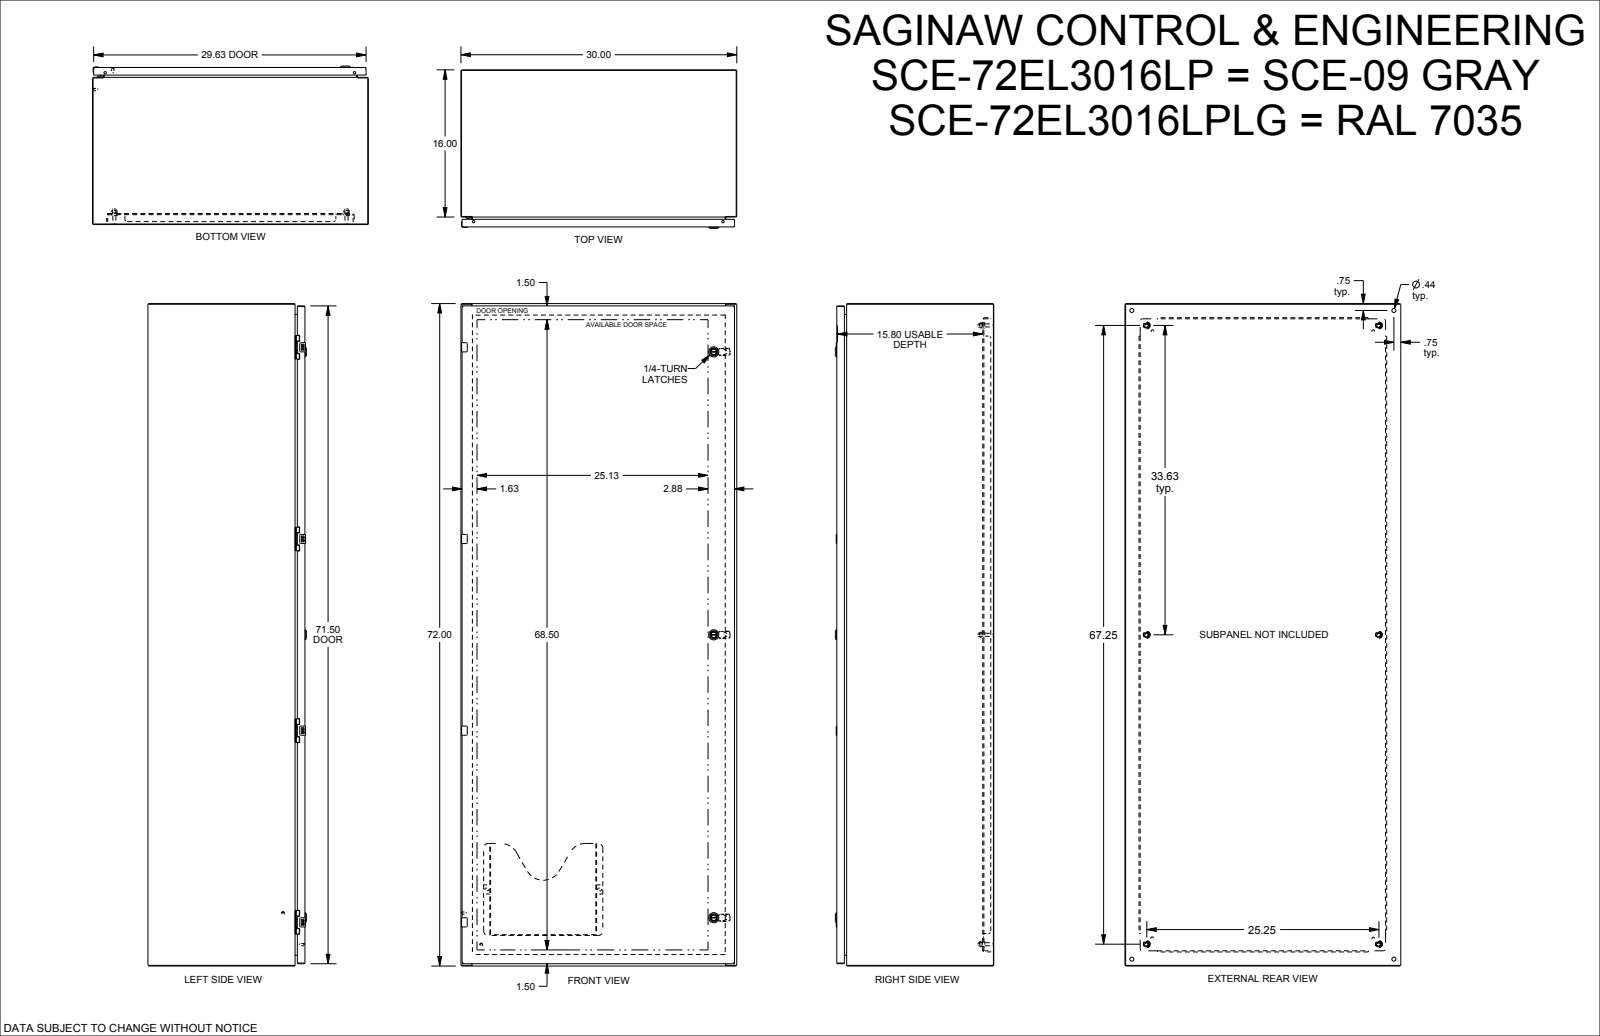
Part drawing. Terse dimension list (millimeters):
name: SCE-72EL3016LP
written by: SolidWorks 2019 (CONFIG_CONTROL_DESIGN)
unit: mm
bodies: 0 solids, 4259 faces (2033 planar, 1208 cylindrical, 1018 other)
size: 1828.8 × 762 × 437.6
holes: 10× ⌀6.8, 8× ⌀4.4, 8× ⌀5.2, 8× ⌀6.2, 8× ⌀9.5, 6× ⌀9.3, 6× ⌀12.7, 4× ⌀1, 4× ⌀4, 4× ⌀5.5, 4× ⌀7.1, 4× ⌀11.1
bosses: 12× ⌀4.3, 8× ⌀6.4, 8× ⌀6.1, 6× ⌀9.3, 6× ⌀8.4, 5× ⌀5, 4× ⌀6.3, 3× ⌀28
rounds: 82× R0.3, 40× R0.3, 40× R0.4, 28× R0.5, 25× R0.8, 20× R0.6, 20× R2.5, 18× R0.8
face distances: 1.9, 760.1, 1.9, 431.7, 429.8, 433.7, 431.7, 3.2, 30.5, 403.2
hole spacings: 529.2, 1058.3, 529.2, 25, 1587.5, 0.5, 12.5, 12.5
